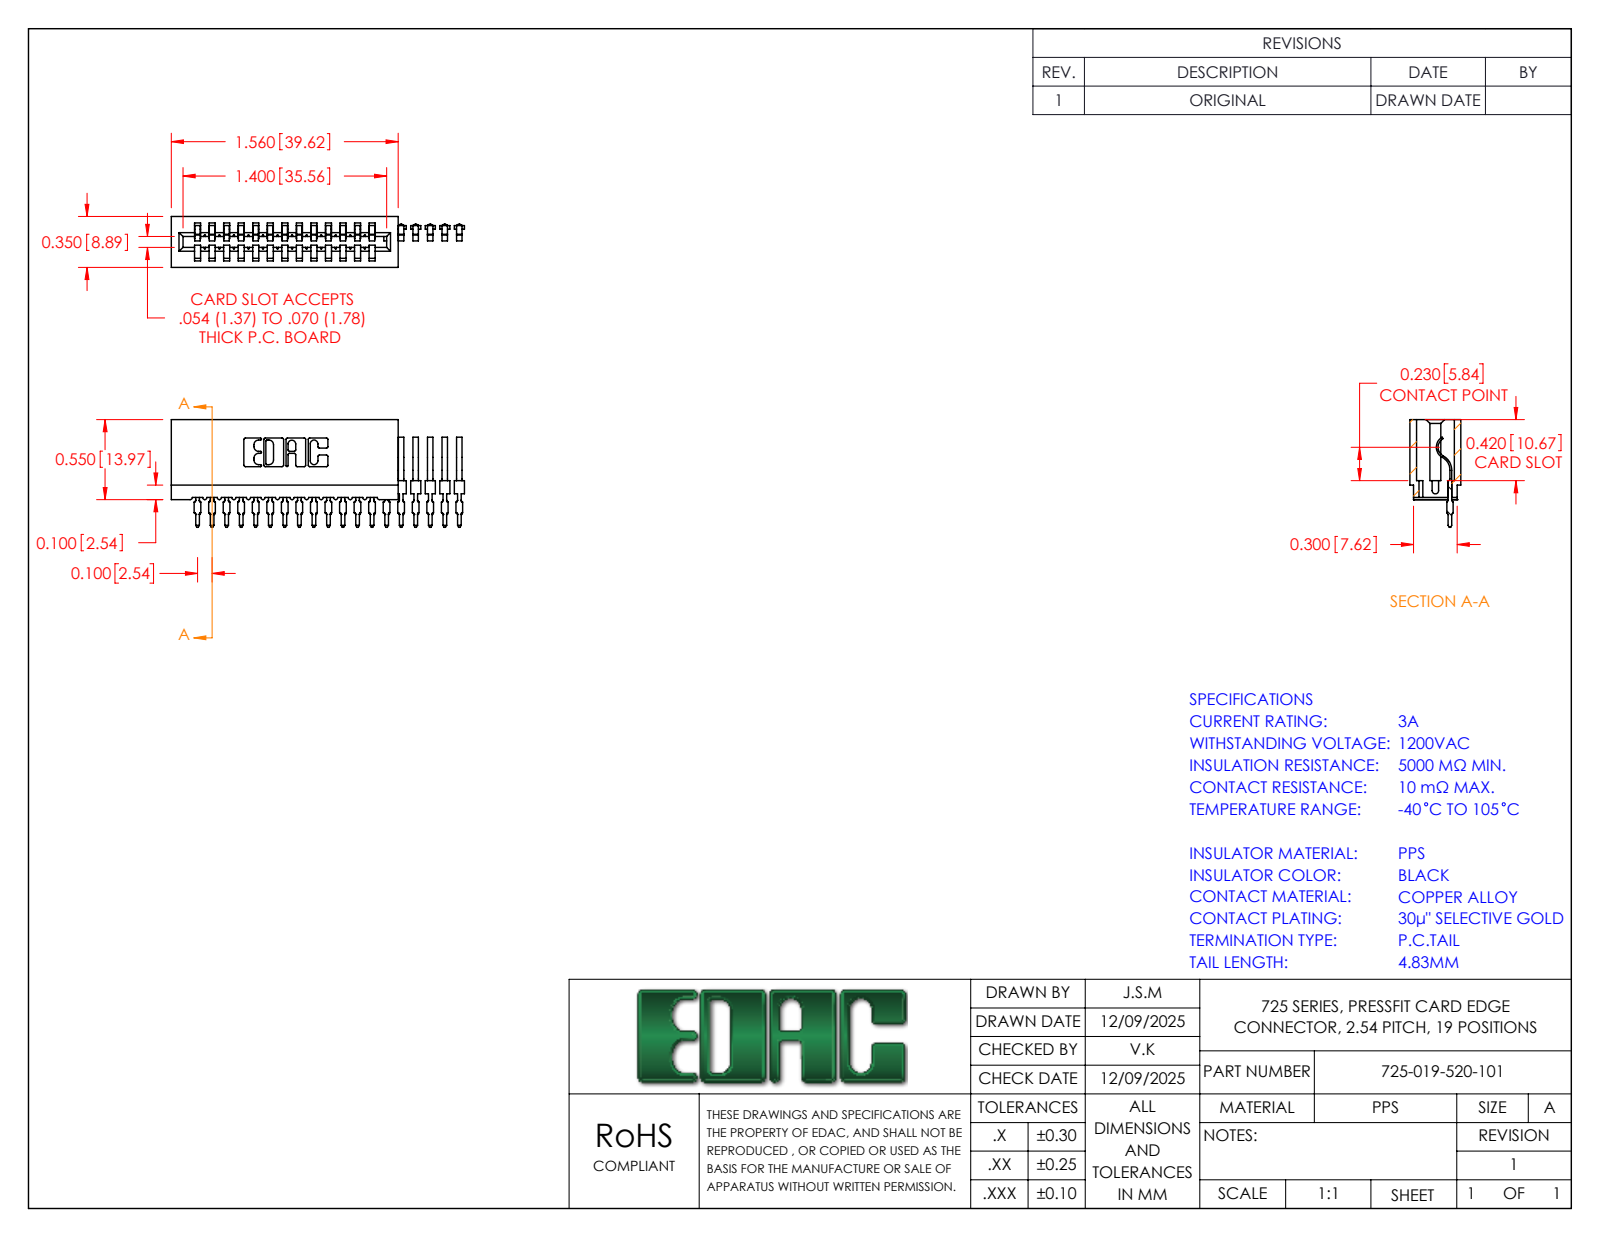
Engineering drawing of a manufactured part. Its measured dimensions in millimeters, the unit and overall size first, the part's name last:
Units: millimetres
Overall size (bounding box): 54.86 × 18.8 × 8.89
Partial cylindrical surfaces — rounded edges, fillets, slot ends (radius × count): R0.38 ×38, R0.55 ×38, R0.25 ×22, R0.17 ×6, R0.8 ×6, R0.13 ×4, R0.28 ×4, R0.67 ×3
Main face-to-face distances: 2.54, 5.08, 7.62, 10.16, 12.7, 15.24, 17.78, 20.32, 8.89, 22.86
Volume: 4 260 mm³ · Surface area: 7 647 mm²
Bodies: 20 solids, 2223 faces (1328 planar, 401 cylindrical, 494 other)
Part name (STEP PRODUCT): 725 Part_Insulator Option - 01; 725-019-520-101; 745-292-001_520
STEP written by: SolidWorks 2023 (CONFIG_CONTROL_DESIGN)
